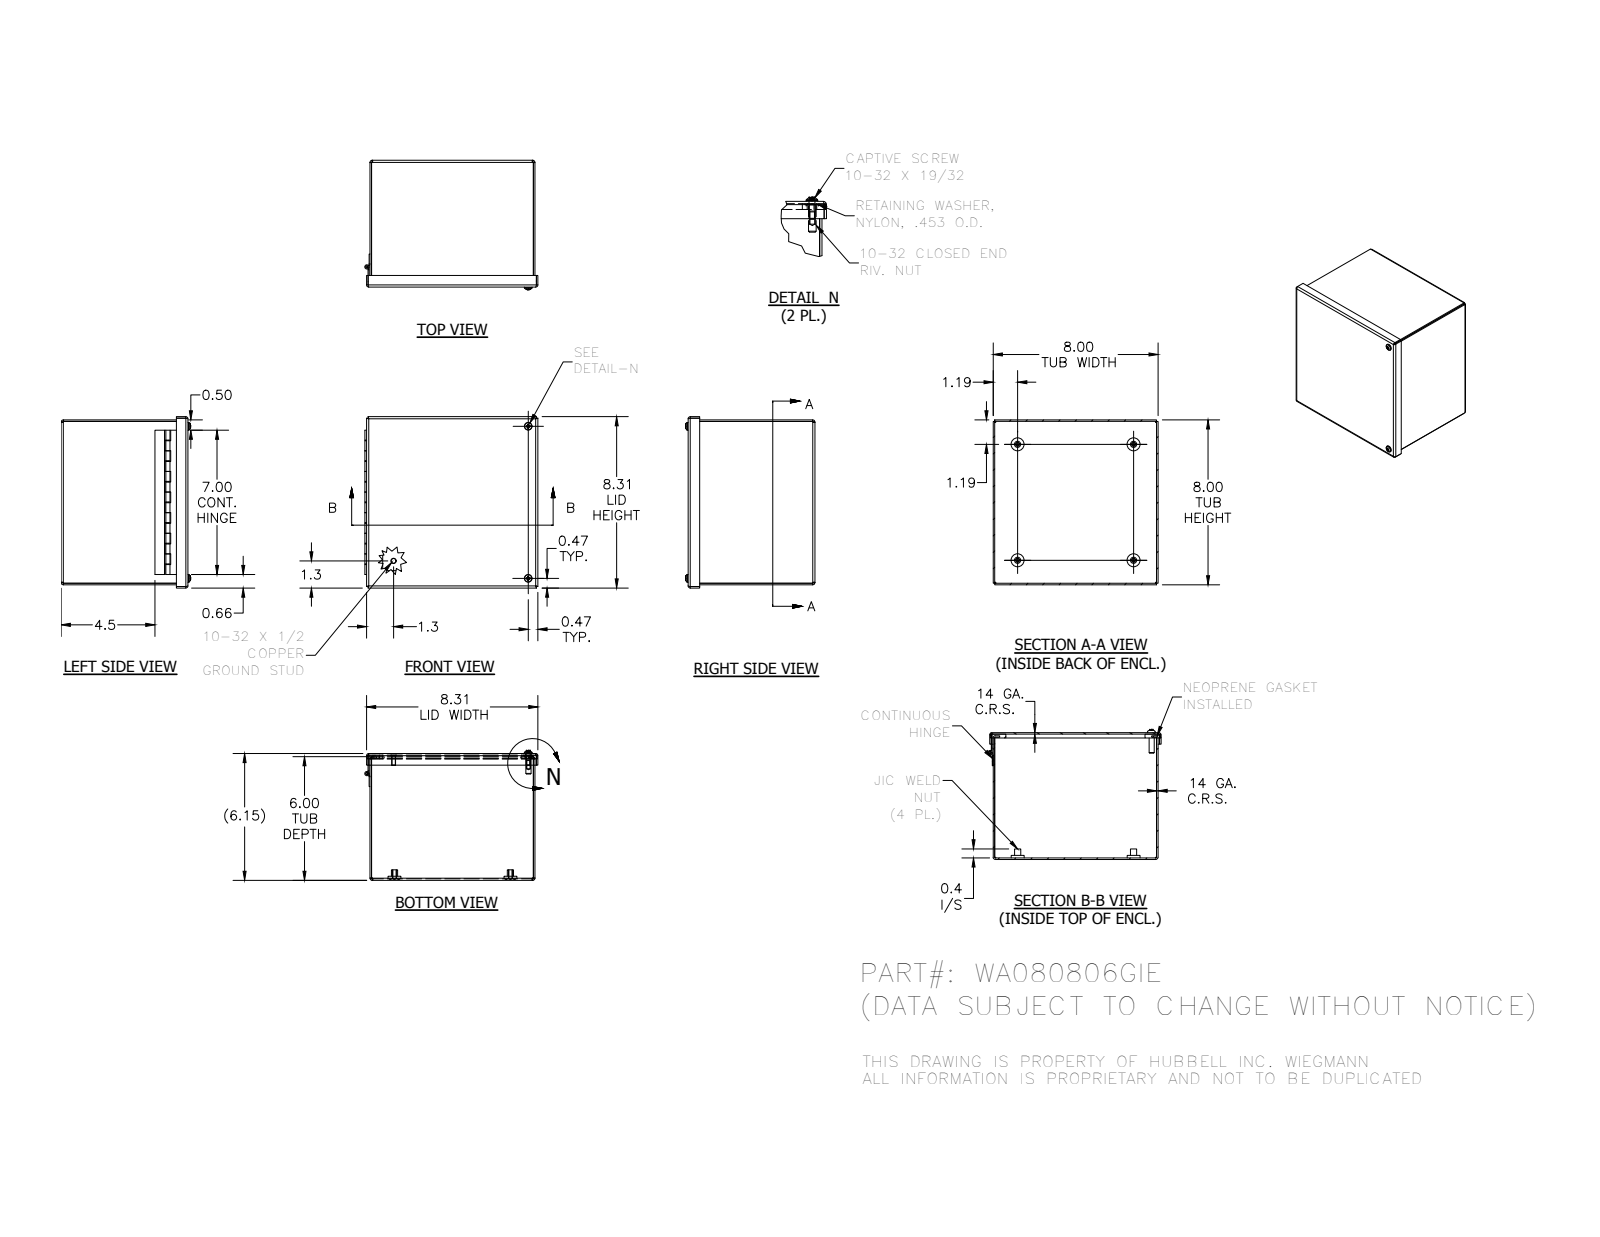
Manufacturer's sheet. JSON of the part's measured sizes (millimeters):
{"part_name": "WA080806GIEBKP; 3499; 328121LH; 328121P (+8 more)", "step_written_by": "Autodesk Inventor 2014 (AUTOMOTIVE_DESIGN)", "units": "millimeters", "bodies": {"solids": 18, "faces": 445, "planar": 257, "cylindrical": 113, "other": 75}, "overall_size": [213.28, 211.14, 159.56], "volume_mm3": 494831, "surface_area_mm2": 505903, "round_holes": [[3.96, 6], [6.53, 4], [7.94, 4], [4.98, 2], [7.06, 2], [7.14, 2], [2.96, 1]], "round_bosses_or_shafts": [[15.88, 4], [7.62, 4], [4.83, 3], [11.51, 2], [10.31, 2], [9.47, 2], [6.3, 2], [6.35, 1]], "partial_cylinders_radius": [[0.79, 12], [2.67, 12], [1.78, 8], [2.27, 2]], "face_to_face_distances": [1.88, 201.32, 154.38, 203.2, 199.44, 152.5, 156.26, 4.76, 6.64, 149.62], "hole_center_spacings": [187.32, 166.59, 31.42, 142.88, 187.31, 187.61, 233.49, 264.91]}
